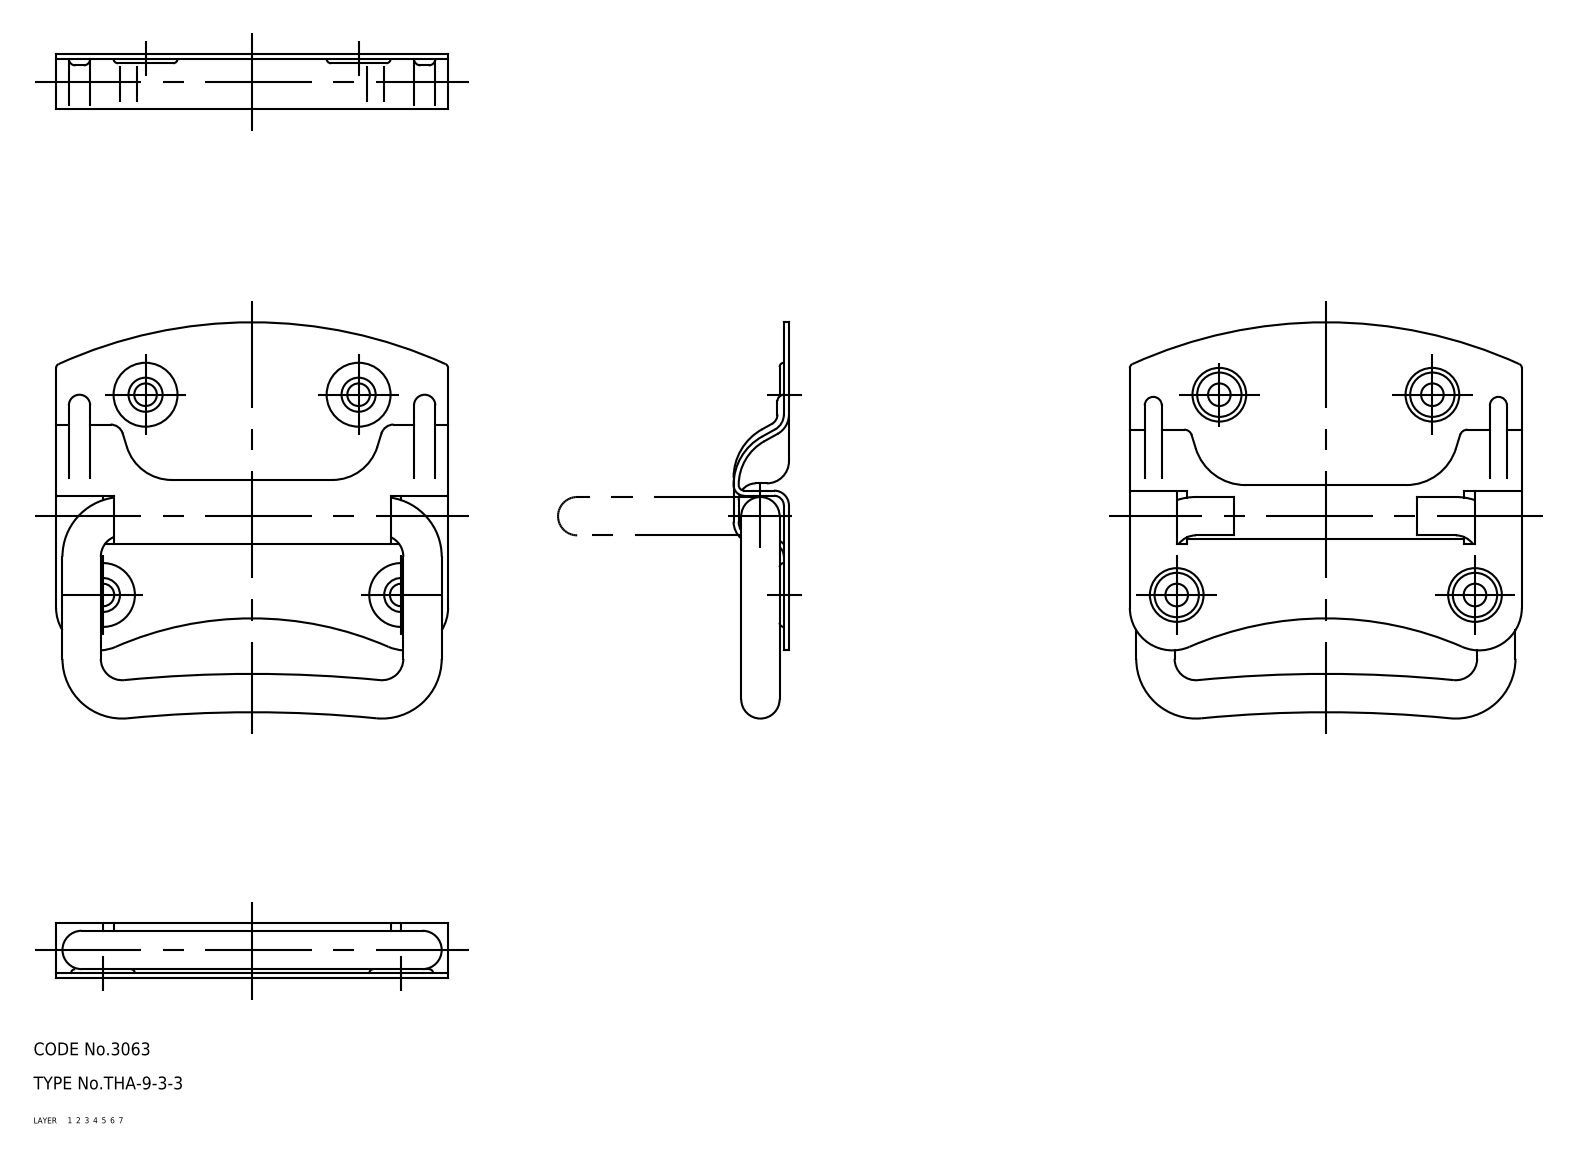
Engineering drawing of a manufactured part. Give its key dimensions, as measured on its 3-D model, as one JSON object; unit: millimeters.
{"part_name": "grip; base; THA_9_3_3_3947_36", "step_written_by": "CADfix (AUTOMOTIVE_DESIGN)", "units": "millimeters", "bodies": {"solids": 2, "faces": 286, "planar": 0, "cylindrical": 0, "other": 286}, "overall_size": [93, 92, 13], "volume_mm3": 21055, "surface_area_mm2": 21822}
